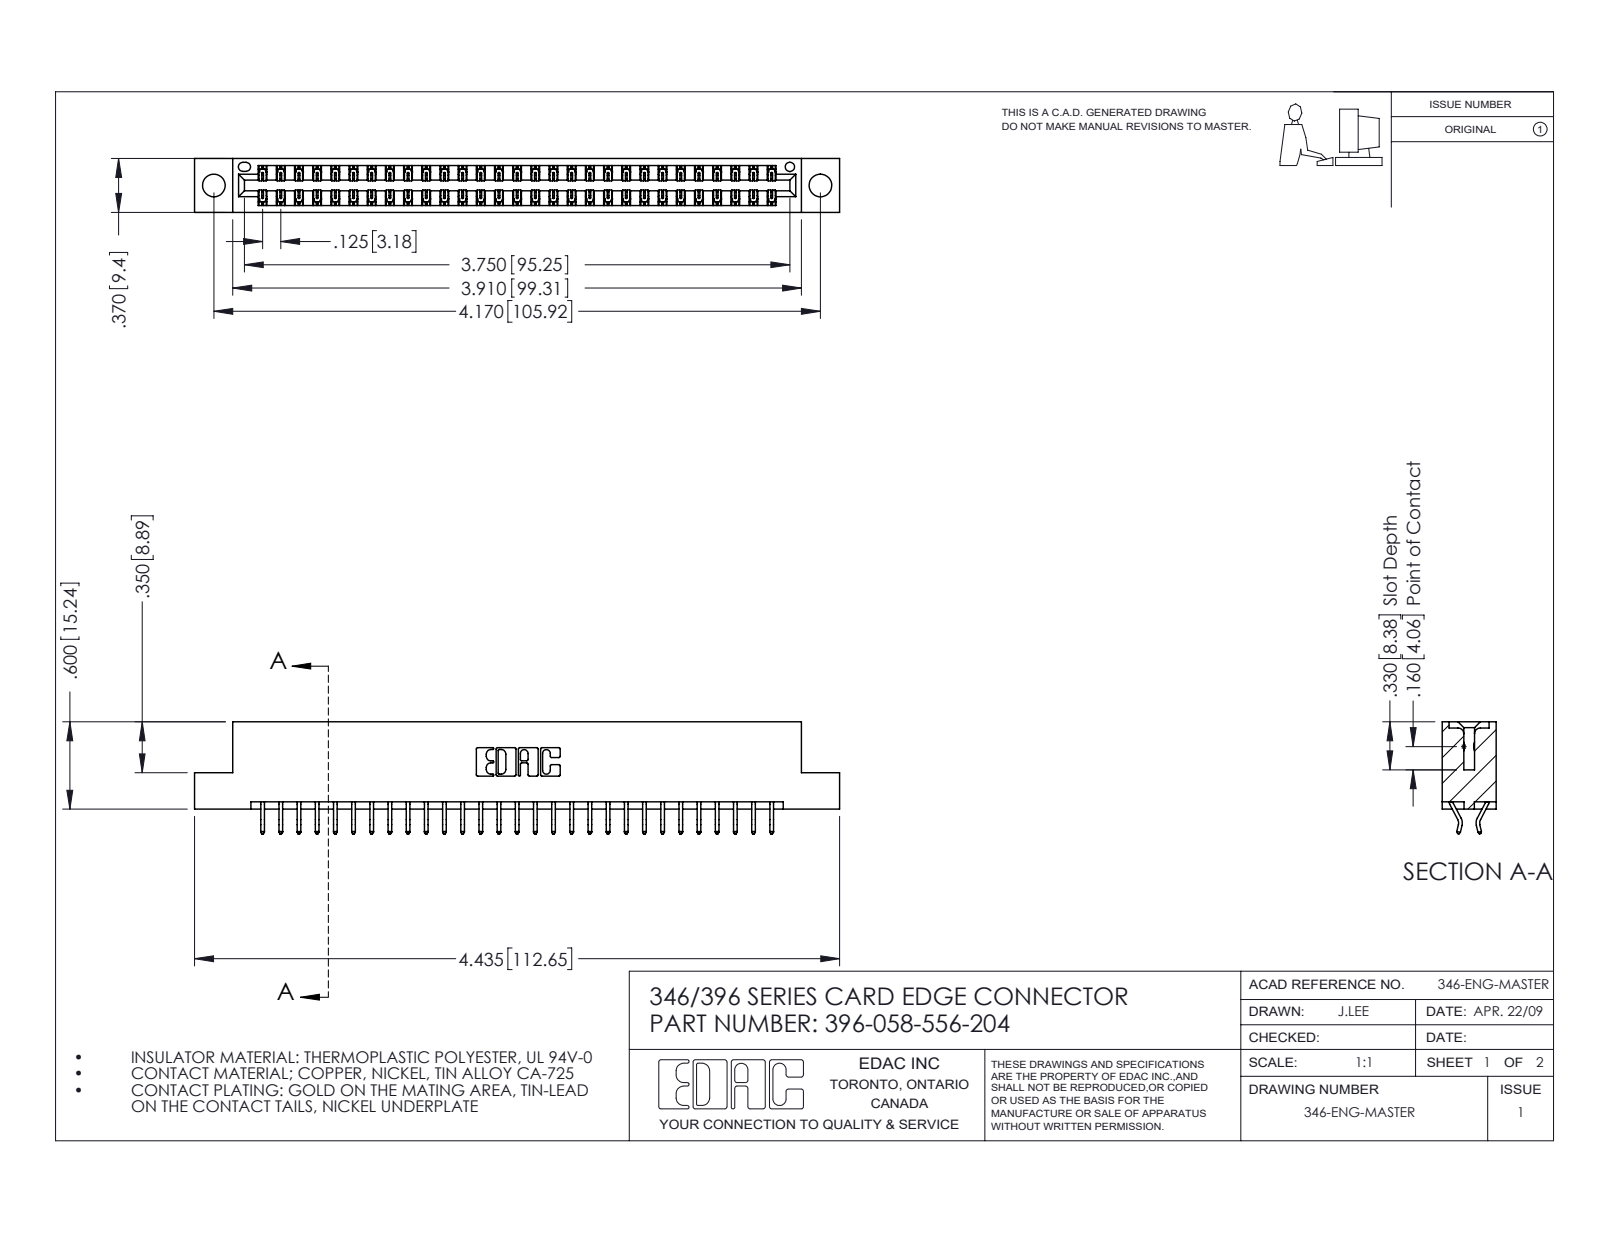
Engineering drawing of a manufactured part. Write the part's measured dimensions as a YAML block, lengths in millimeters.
part_name: "346 Part_Flush Mounting Lugs - 0.156 Dia-TH; 345-292-001_556 Tail; 396-058-556-204"
step_written_by: "SolidWorks 2016 (CONFIG_CONTROL_DESIGN)"
units: millimeters
bodies: {solids: 59, faces: 3486, planar: 2338, cylindrical: 1148, other: 0}
overall_size: [112.6, 19.6, 9.4]
volume: 10800
surface_area: 14390
round_holes:
  - {diameter: 4, count: 2}
  - {diameter: 1.6, count: 1}
partial_cylinders:
  - {radius: 0.2, count: 87}
  - {radius: 0.3, count: 22}
  - {radius: 0.2, count: 6}
  - {radius: 0.8, count: 6}
  - {radius: 0.7, count: 3}
  - {radius: 0.3, count: 2}
  - {radius: 0.4, count: 2}
  - {radius: 0.6, count: 2}
face_to_face_distances: [1.2, 8.2, 9.4, 6.4, 0.6, 1.8, 7.6, 7, 3.8, 5.6]
hole_center_spacings: [6.2, 100.6, 105.9]
